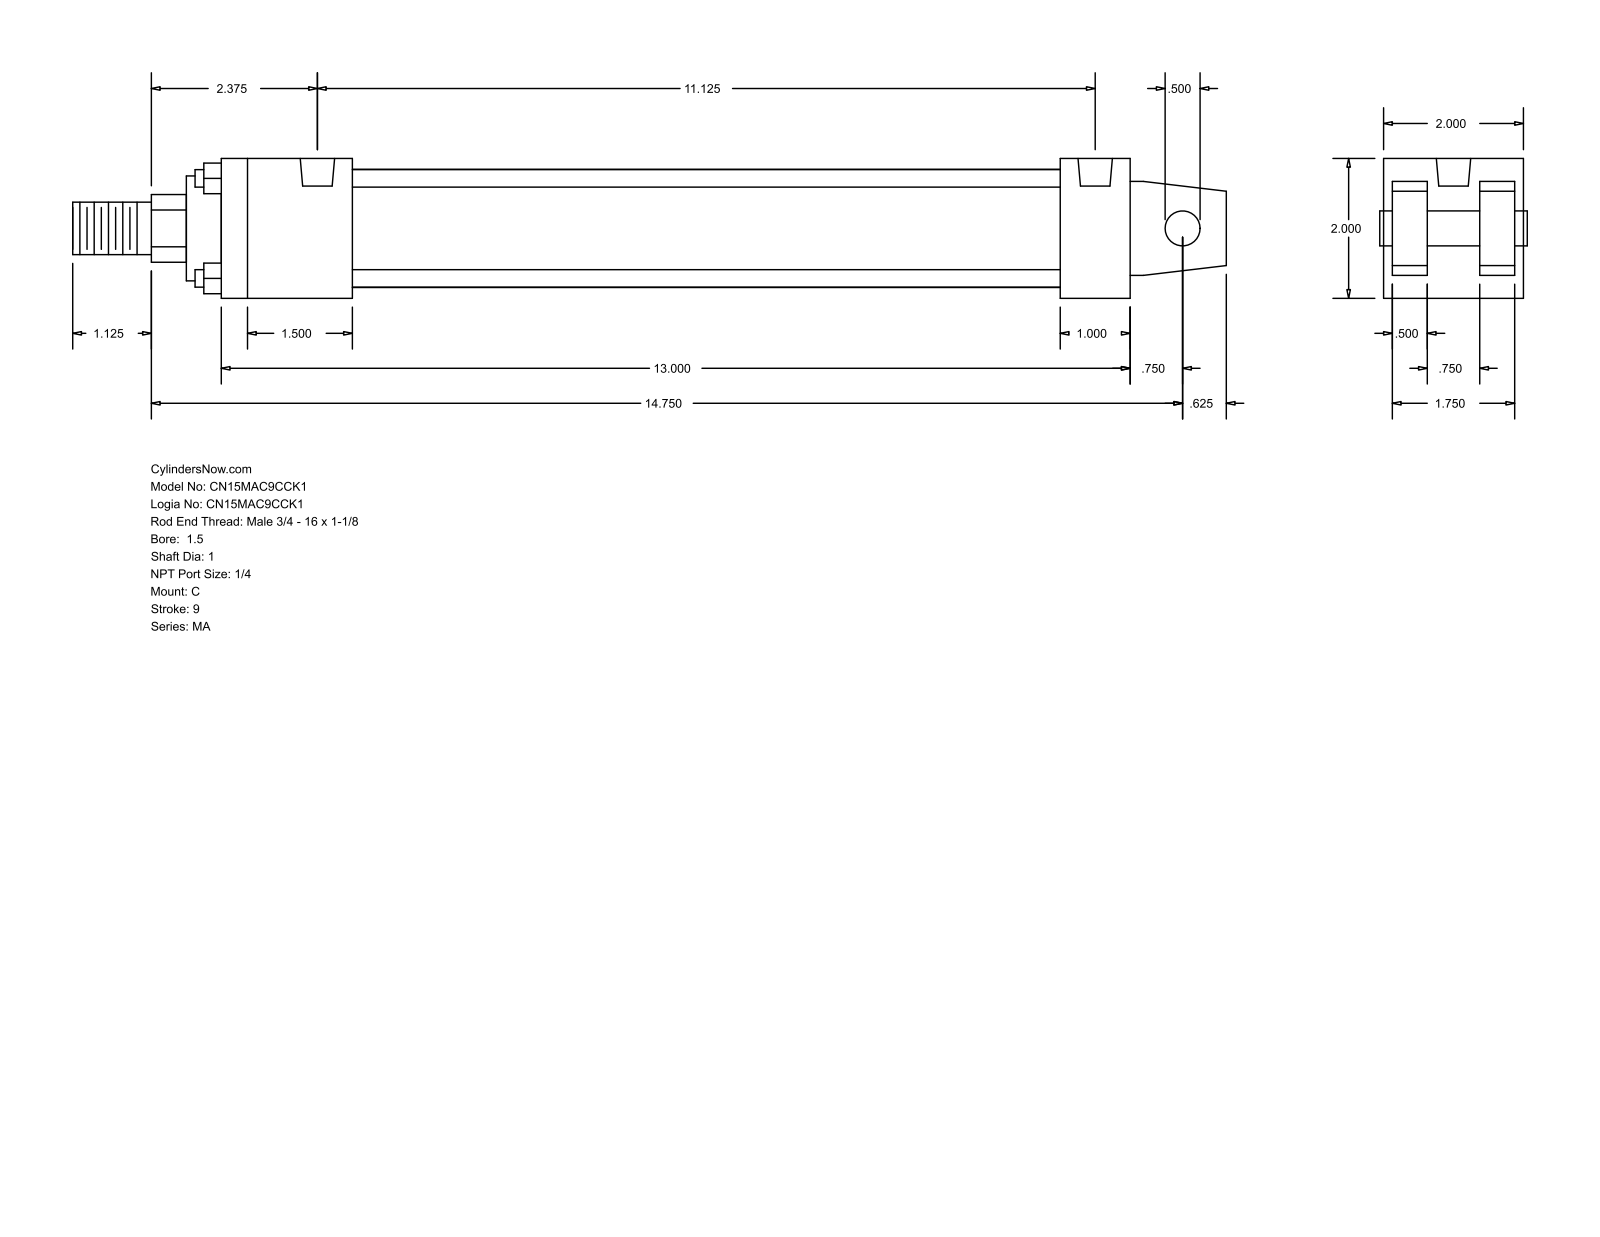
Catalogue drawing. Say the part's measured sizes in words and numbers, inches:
The part is named "MA_C__0150_1". Its 3-D file was written by "GSSL Pune (CONFIG_CONTROL_DESIGN)". It is 0 solids with 103 faces: 76 planar, 27 cylindrical and 0 other. Overall it measures 16.5 by 2 by 2 inches. Round holes: 4 of diameter 0.313, 2 of diameter 0.492. Round bosses or shafts: 4 of diameter 0.25, 1 of diameter 1.69, 1 of diameter 1.5, 1 of diameter 1, 1 of diameter 0.75, 1 of diameter 0.5. Partial cylindrical surfaces (rounded edges, fillets, slot ends): 1 of radius 0.484. The main face-to-face distances are 2, 1.875, 0.5, 0.125, 0.625, 1.375, 1.25, 13, 1, 12. The hole center spacings are 11.125.
